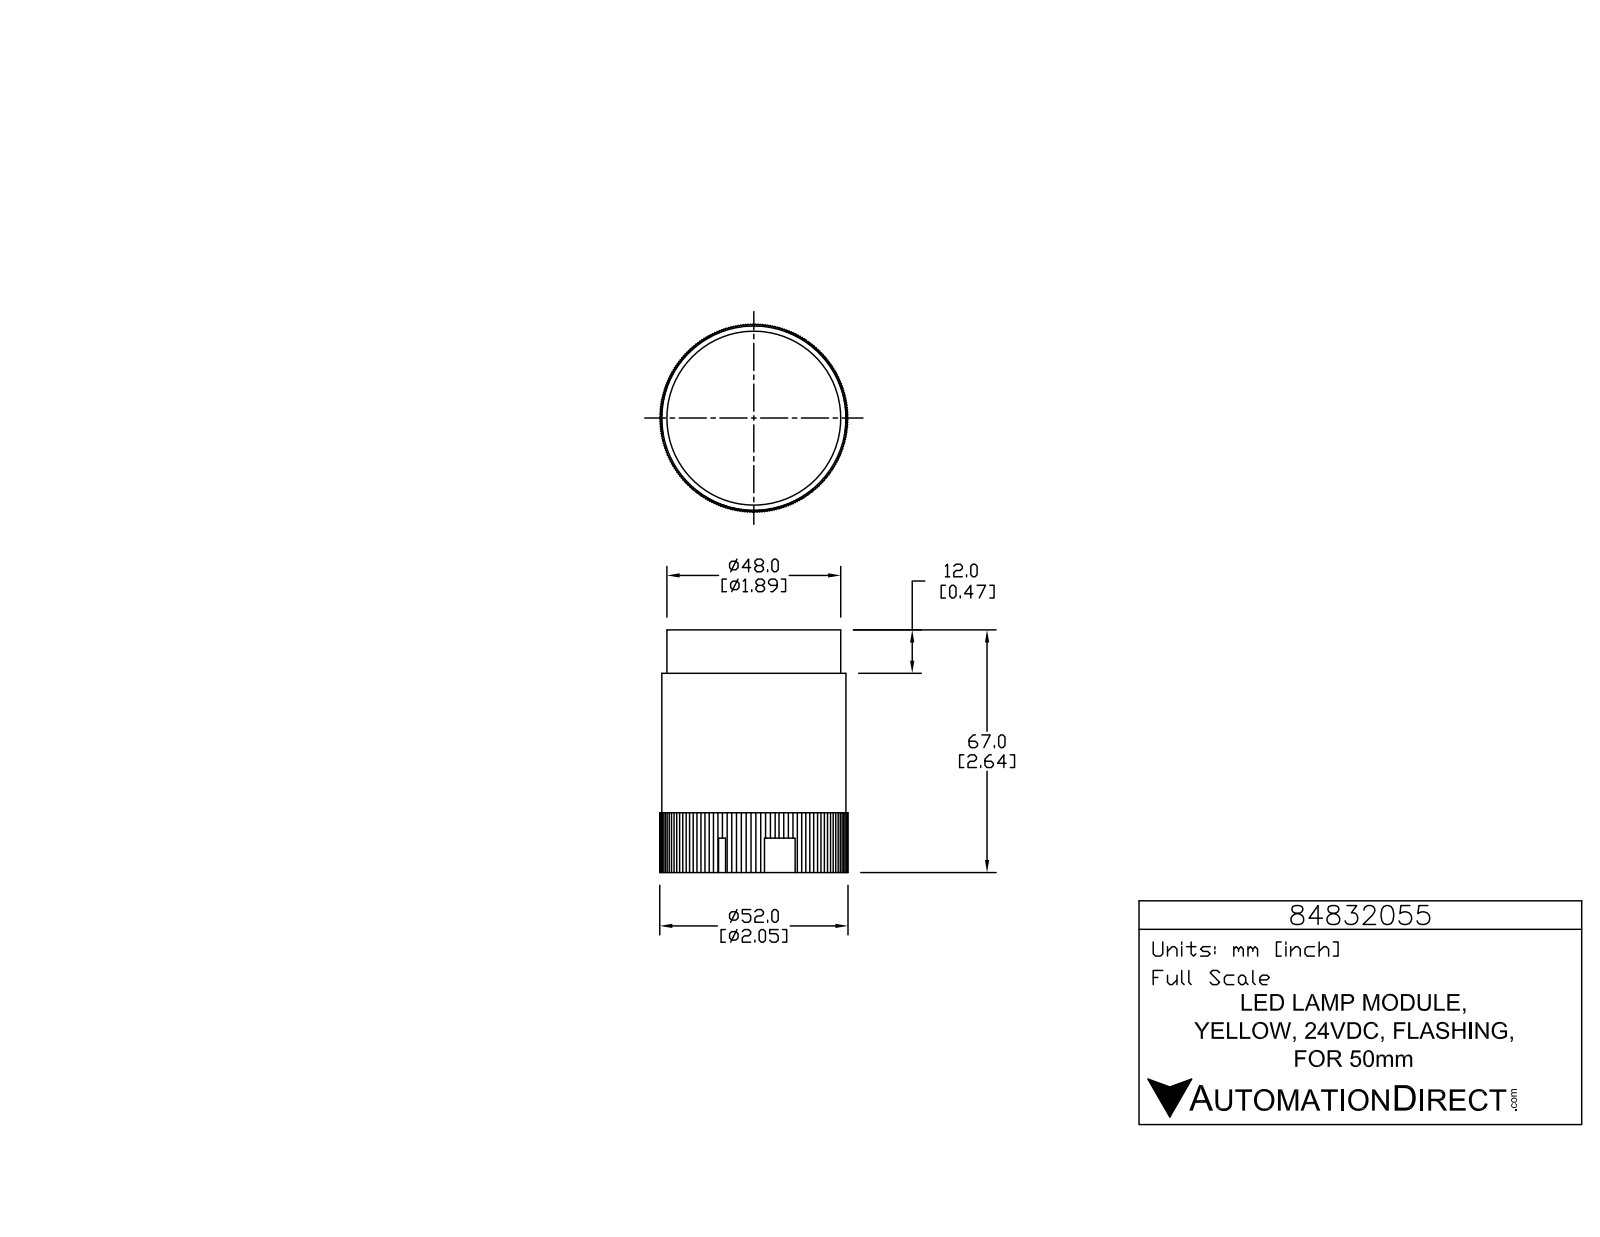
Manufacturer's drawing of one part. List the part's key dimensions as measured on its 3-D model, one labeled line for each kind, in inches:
Part name (STEP PRODUCT): 84832055
STEP written by: SolidWorks 2015 (AUTOMOTIVE_DESIGN)
Units: inches
Bodies: 1 solid, 1265 faces (1020 planar, 245 cylindrical, 0 other)
Overall size (bounding box): 2.638 × 2.047 × 2.047
Volume: 6.873 in³ · Surface area: 27.62 in²
Round holes (diameter × count): ⌀0.039 ×3, ⌀1.898 ×1
Round bosses / shafts (diameter × count): ⌀0.226 ×3, ⌀0.056 ×3, ⌀2.002 ×1, ⌀1.89 ×1
Partial cylindrical surfaces — rounded edges, fillets, slot ends (radius × count): R0.008 ×6, R0.008 ×6, R0.008 ×6, R0.131 ×6, R0.004 ×3, R0.005 ×3, R0.008 ×3, R0.008 ×3
Main face-to-face distances: 2.165, 1.428, 1.429, 1.429, 0.472, 2.638, 1.428, 1.428, 1.693, 1.988
